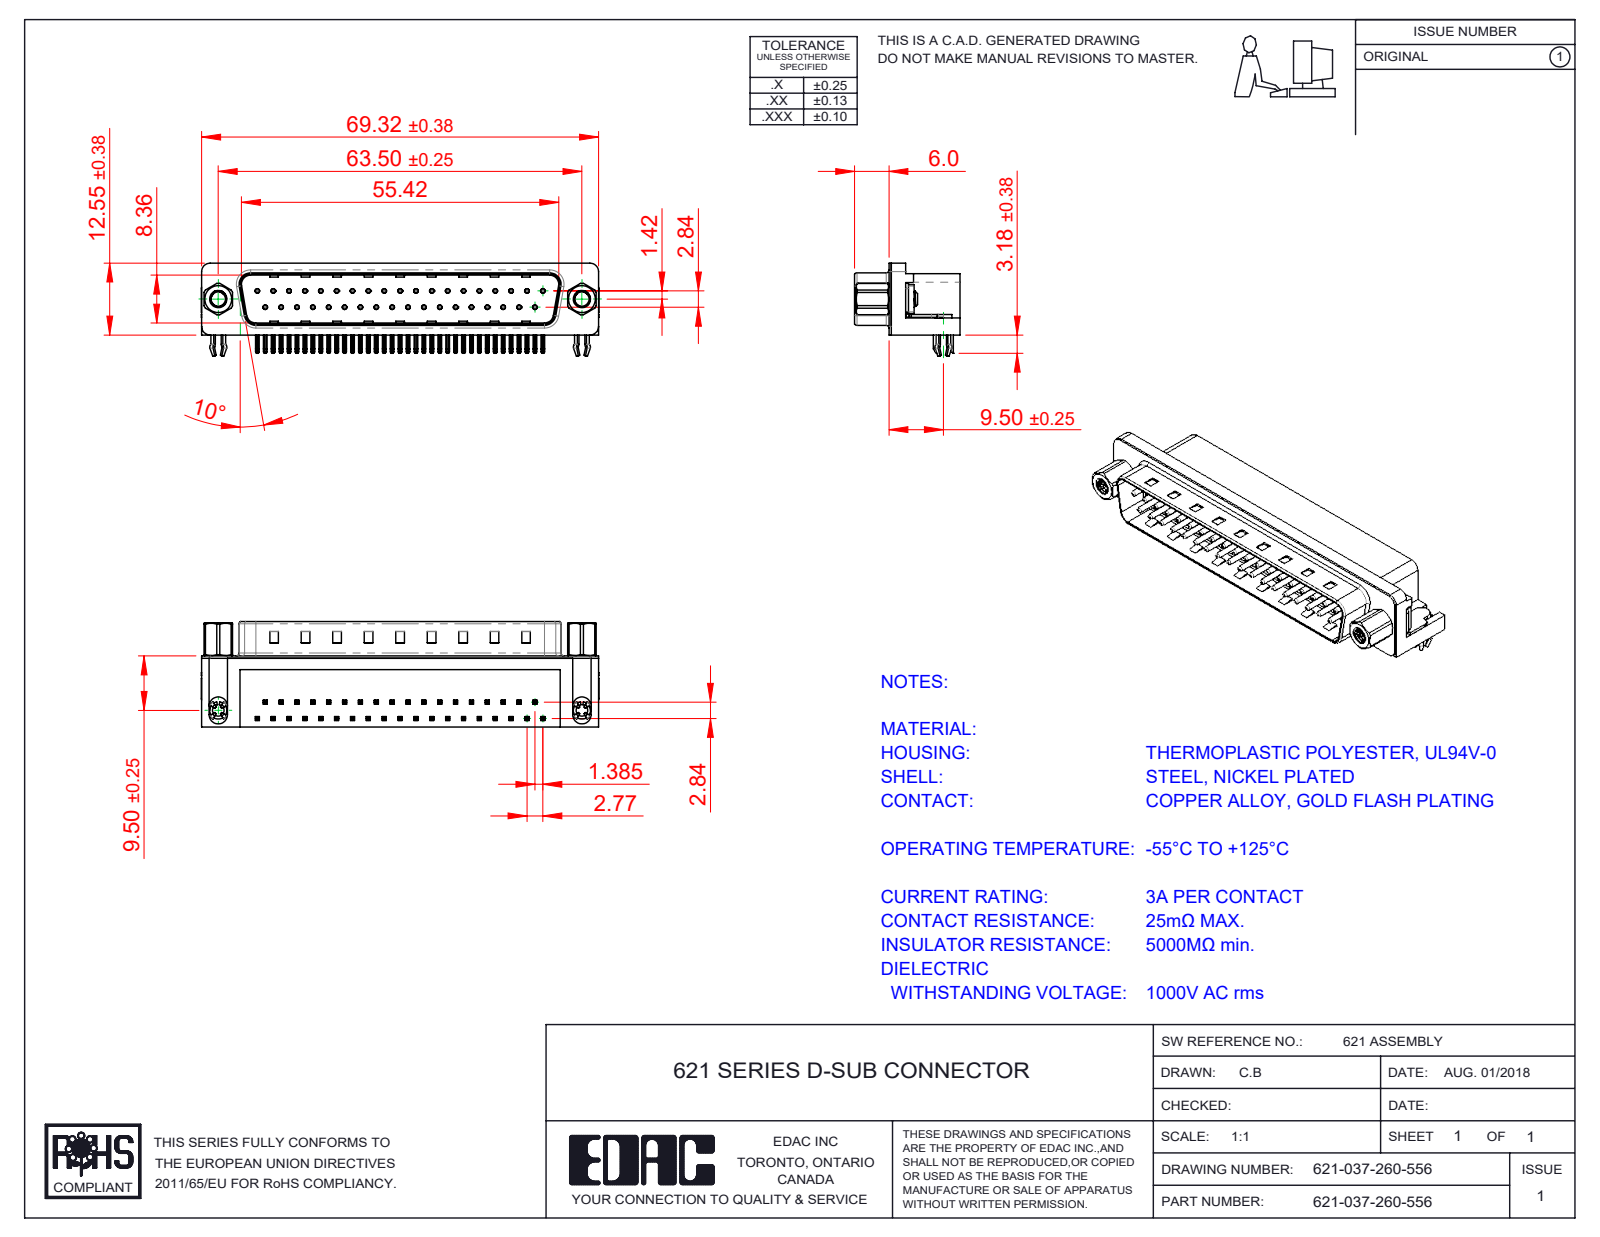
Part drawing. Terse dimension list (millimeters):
name: 621 M3 Threaded Rivet; 621 Contact Top; 621-037-260-556; 621 4-40 Threaded Board Mount (+4 more)
written by: SolidWorks 2016 (CONFIG_CONTROL_DESIGN)
unit: mm
bodies: 45 solids, 3377 faces (2035 planar, 1023 cylindrical, 319 other)
size: 69.4 × 18.4 × 15.73
volume: 8 872 mm³; area: 10 706 mm²
holes: 37× ⌀0.35, 37× ⌀0.8, 2× ⌀2.26, 2× ⌀2.5, 2× ⌀4, 2× ⌀4.8, 2× ⌀5
bosses: 37× ⌀0.75, 2× ⌀4.9, 2× ⌀4.75, 2× ⌀3.9, 2× ⌀3.26, 2× ⌀3
rounds: 156× R0.25, 74× R0.12, 16× R1, 9× R0.5, 8× R1.6, 7× R1.5, 4× R0.9, 4× R2
face distances: 0.4, 12, 10.35, 8.76, 2.1, 1.7, 10.46, 10.86, 9, 12.4
hole spacings: 3.16, 2.77, 5.54, 8.31, 11.08, 13.85, 19.39, 22.16
